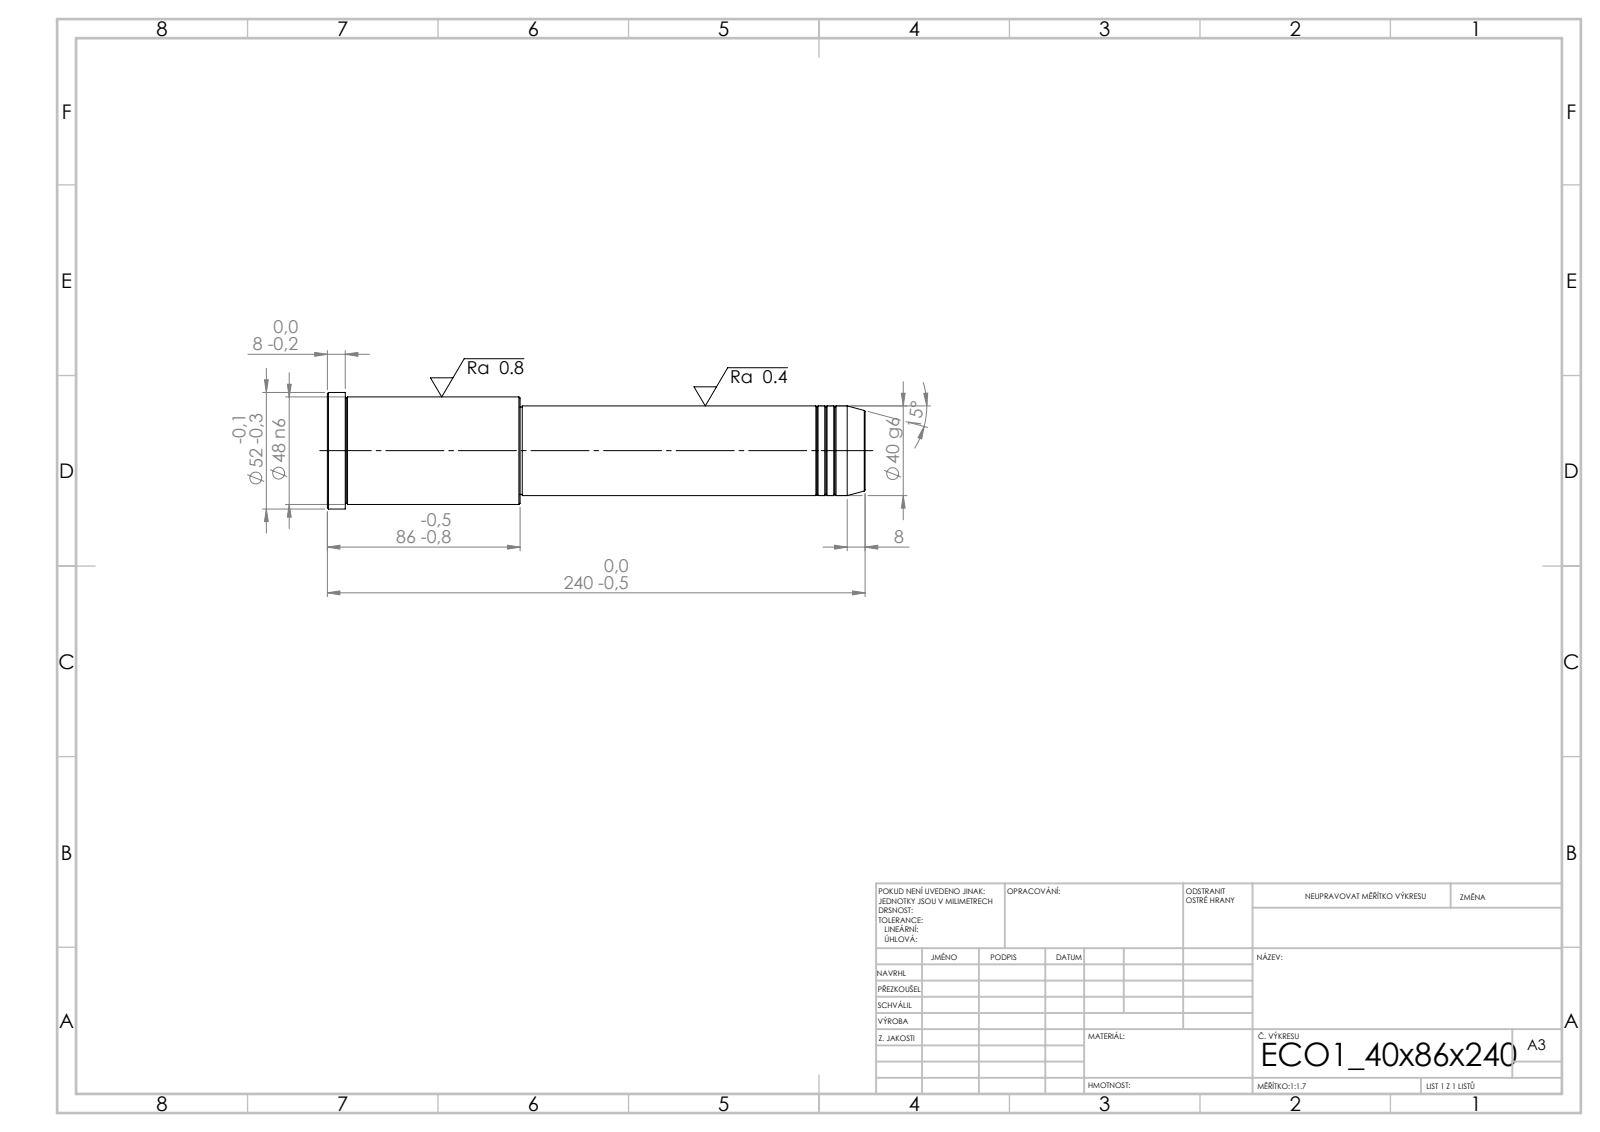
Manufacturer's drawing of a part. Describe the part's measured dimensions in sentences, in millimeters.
Its 3-D file was written by "SolidWorks 2019 (CONFIG_CONTROL_DESIGN)". It is 1 solid with 43 faces: 5 planar, 14 cylindrical and 24 other. Overall it measures 240 by 52 by 52 millimeters. Its volume is 350 309 cubic millimeters and its surface area 36 698 square millimeters. Round bosses or shafts: 1 of diameter 52, 1 of diameter 48, 1 of diameter 40, 1 of diameter 39. The main face-to-face distances are 240, 154, 86, 232, 78, 8, 153, 1, 79, 87.
